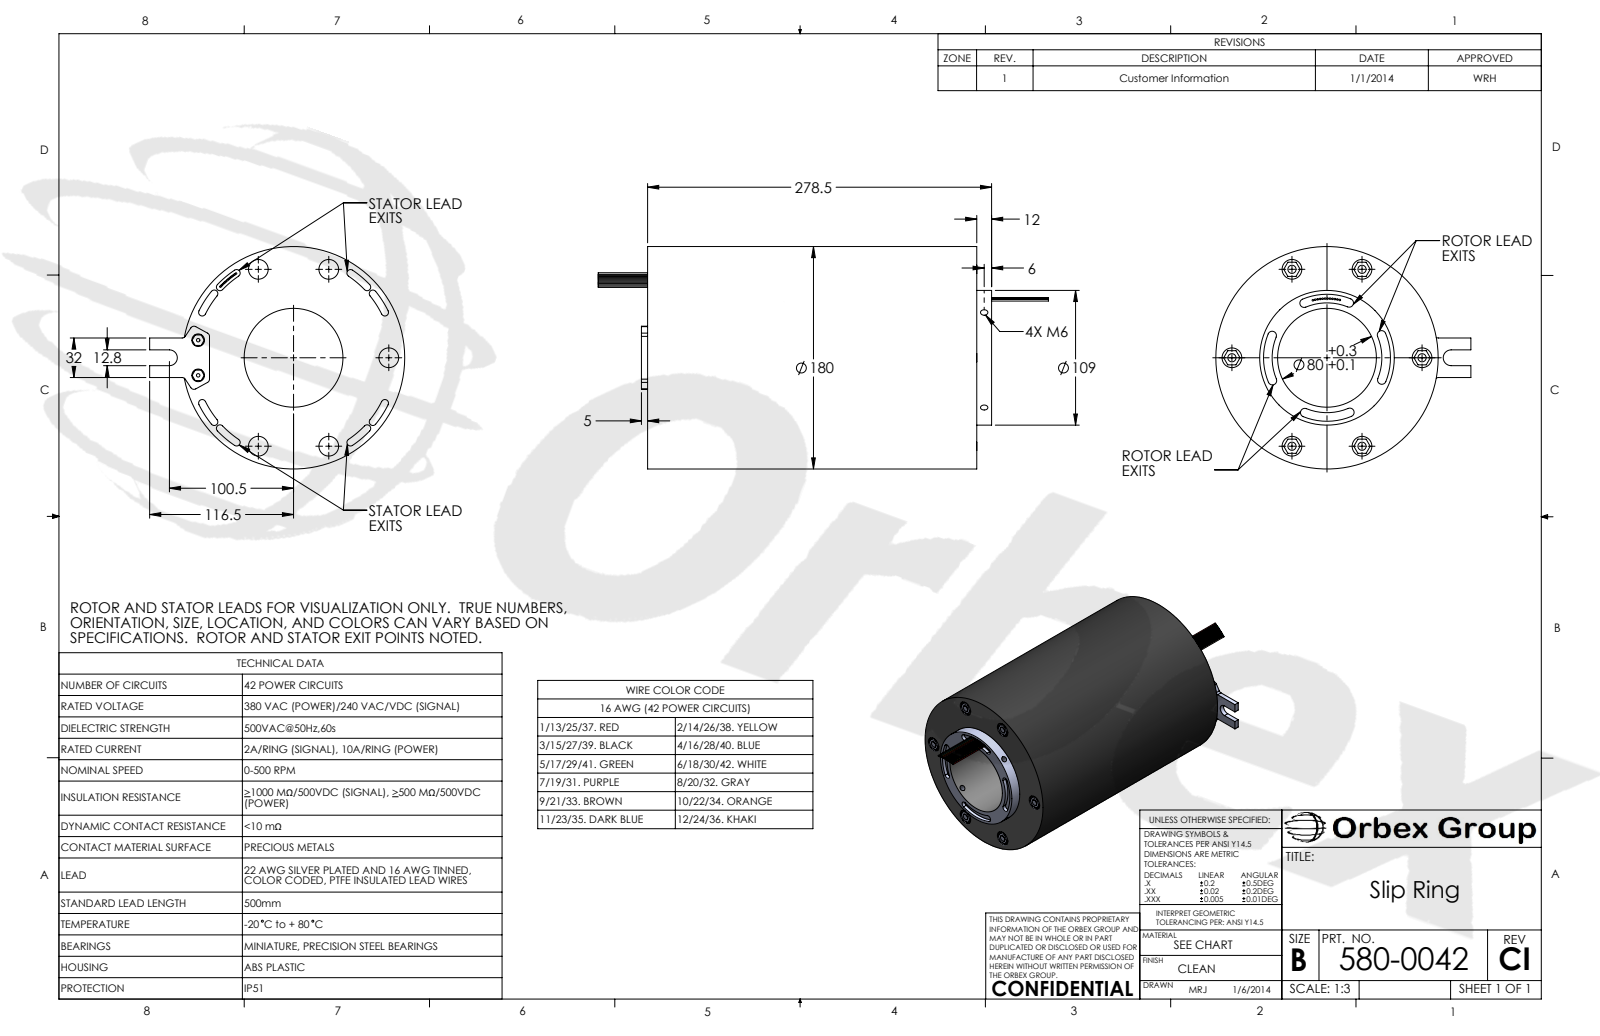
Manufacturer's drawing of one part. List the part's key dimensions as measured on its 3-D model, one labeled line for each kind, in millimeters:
Part name (STEP PRODUCT): 580-0042 Rev CI
STEP written by: SolidWorks 2013 (CONFIG_CONTROL_DESIGN)
Units: millimetres
Bodies: 1 solid, 306 faces (131 planar, 175 cylindrical, 0 other)
Overall size (bounding box): 364.5 × 206.5 × 180
Volume: 5 489 000 mm³ · Surface area: 279 259 mm²
Round holes (diameter × count): ⌀16 ×12, ⌀6 ×4, ⌀2.81 ×2, ⌀10.24 ×2, ⌀80 ×1
Round bosses / shafts (diameter × count): ⌀1.3 ×24, ⌀6.64 ×6, ⌀180 ×1, ⌀109 ×1
Partial cylindrical surfaces — rounded edges, fillets, slot ends (radius × count): R2.92 ×16, R3.48 ×8, R3 ×6, R6.4 ×1, R44.43 ×1, R51.39 ×1, R79.63 ×1, R85.48 ×1
Main face-to-face distances: 266.5, 278.5, 12, 2, 4, 274.5, 264.5, 262.5, 5, 271.5
Hole centre spacings: 127.47, 14.22, 56.88, 76.98, 77.02, 86.41, 86.49, 86.52
